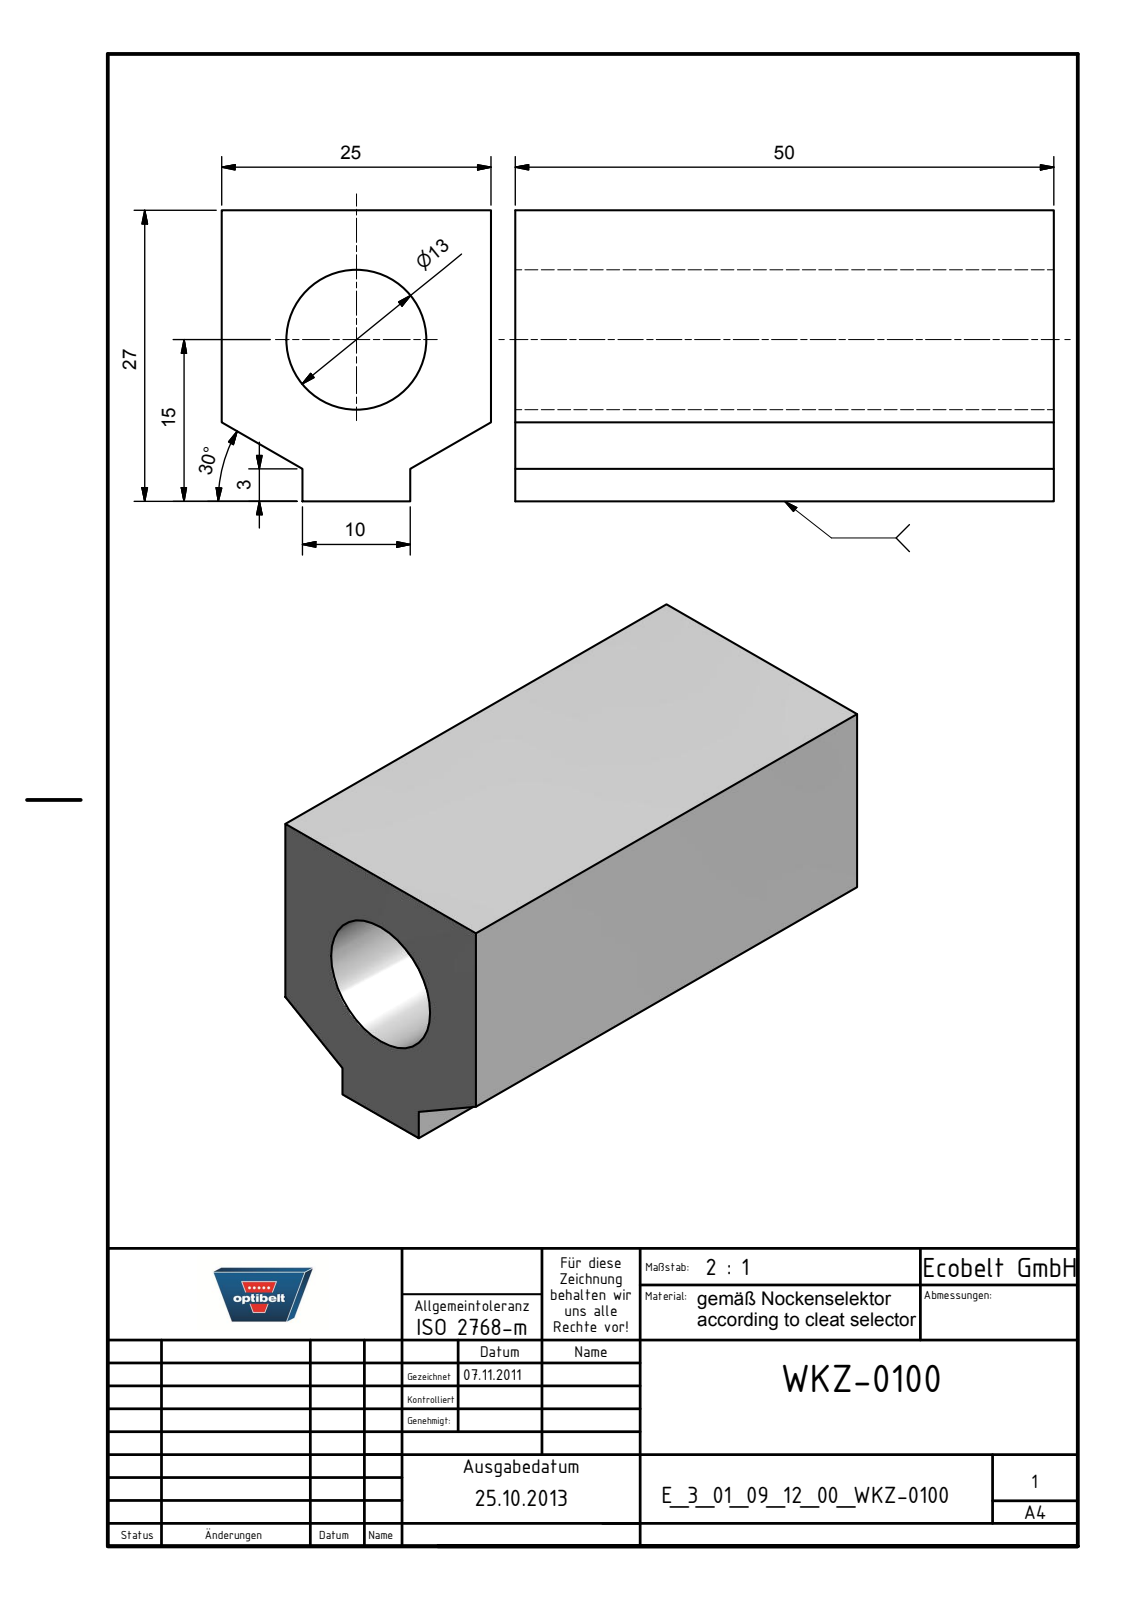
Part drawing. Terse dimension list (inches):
name: E_3_01_09_12_00_WKZ-0100
written by: Autodesk Inventor 2025 (AUTOMOTIVE_DESIGN)
unit: in
bodies: 1 solid, 11 faces (10 planar, 1 cylindrical, 0 other)
size: 1.969 × 1.063 × 0.984
volume: 1.418 in³; area: 12.18 in²
holes: 1× ⌀0.512
face distances: 0.984, 1.063, 1.969, 0.295, 0.689, 0.394
